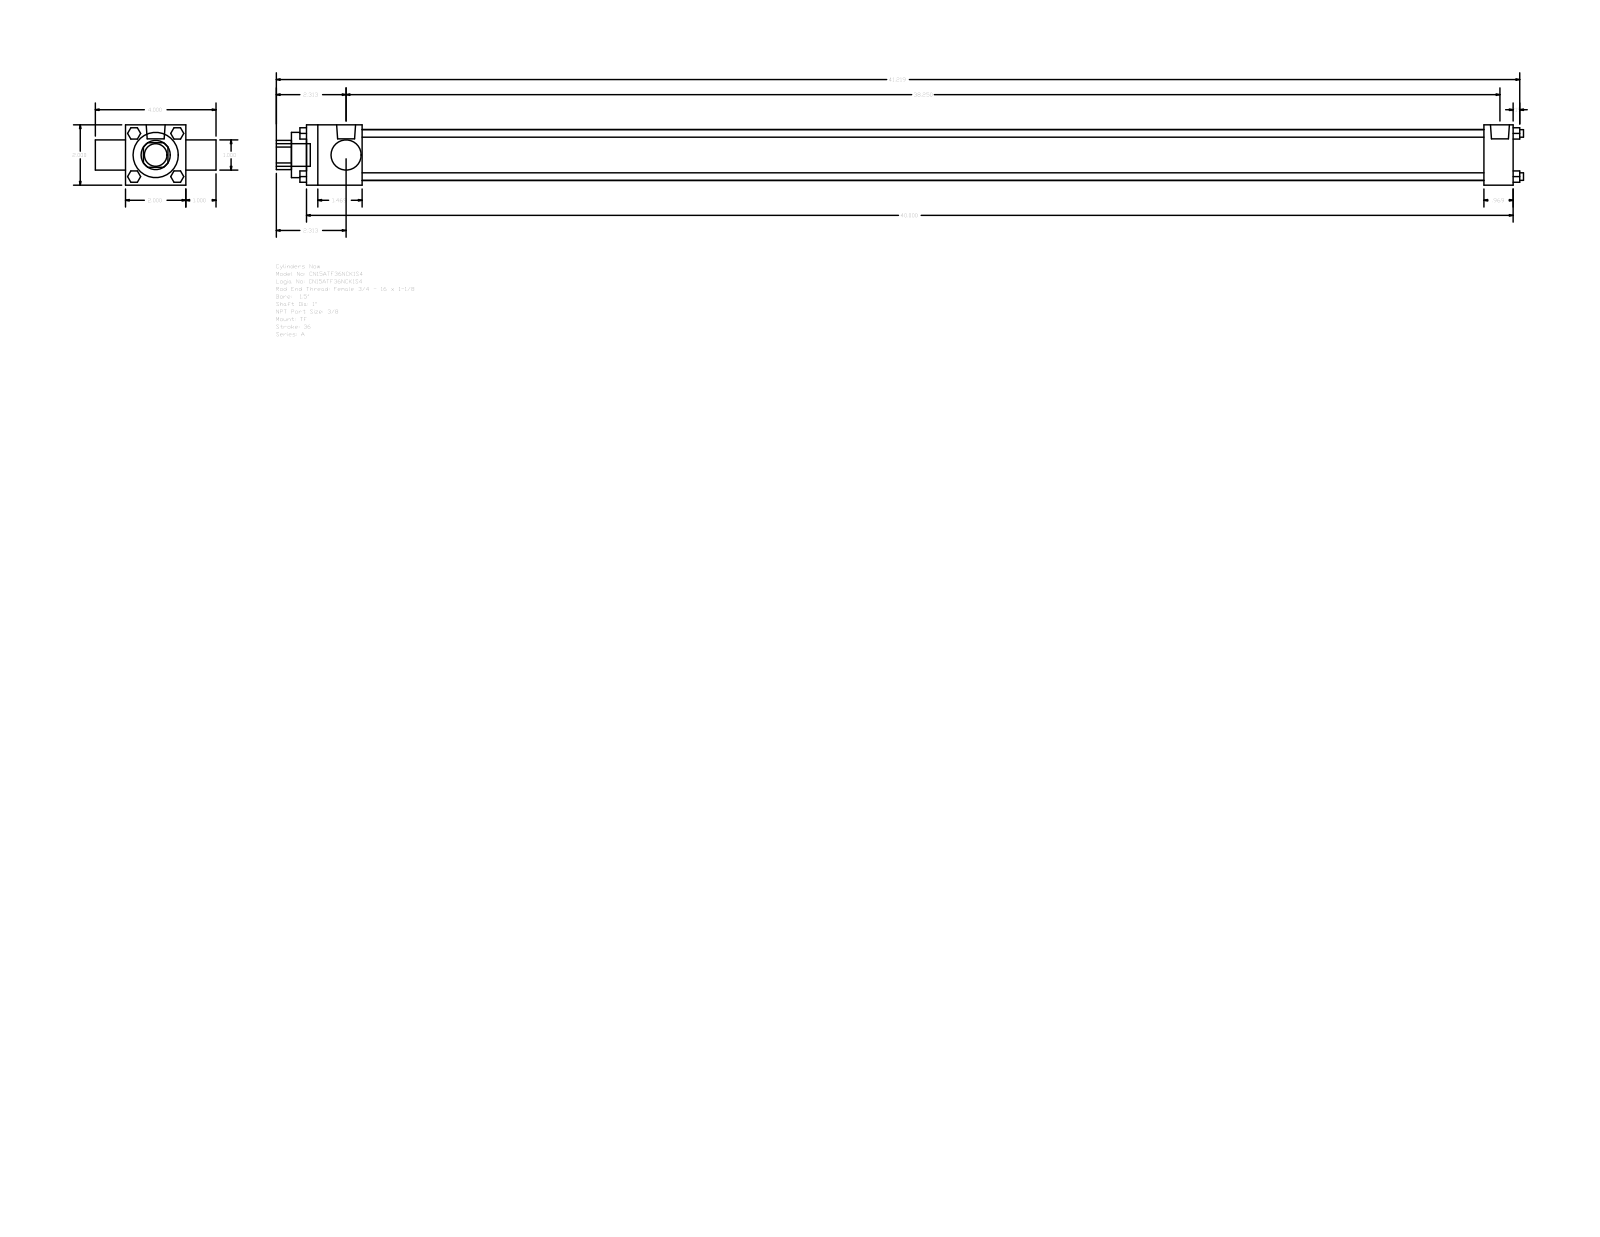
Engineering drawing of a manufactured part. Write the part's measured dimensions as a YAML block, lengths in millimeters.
part_name: "A_TF__0150_1"
step_written_by: "GSSL Pune (CONFIG_CONTROL_DESIGN)"
units: millimeters
bodies: {solids: 0, faces: 120, planar: 92, cylindrical: 28, other: 0}
overall_size: [1050.13, 101.6, 50.8]
round_holes:
  - {diameter: 25.4, count: 2}
  - {diameter: 38.1, count: 1}
  - {diameter: 42.93, count: 1}
round_bosses_or_shafts:
  - {diameter: 6.35, count: 4}
  - {diameter: 5.56, count: 3}
  - {diameter: 15.93, count: 2}
  - {diameter: 19.05, count: 1}
partial_cylinders:
  - {radius: 12.29, count: 1}
face_to_face_distances: [50.8, 25.4, 1016, 76.2, 46.83, 991.39, 944.56, 969.17, 24.61, 12.7]
